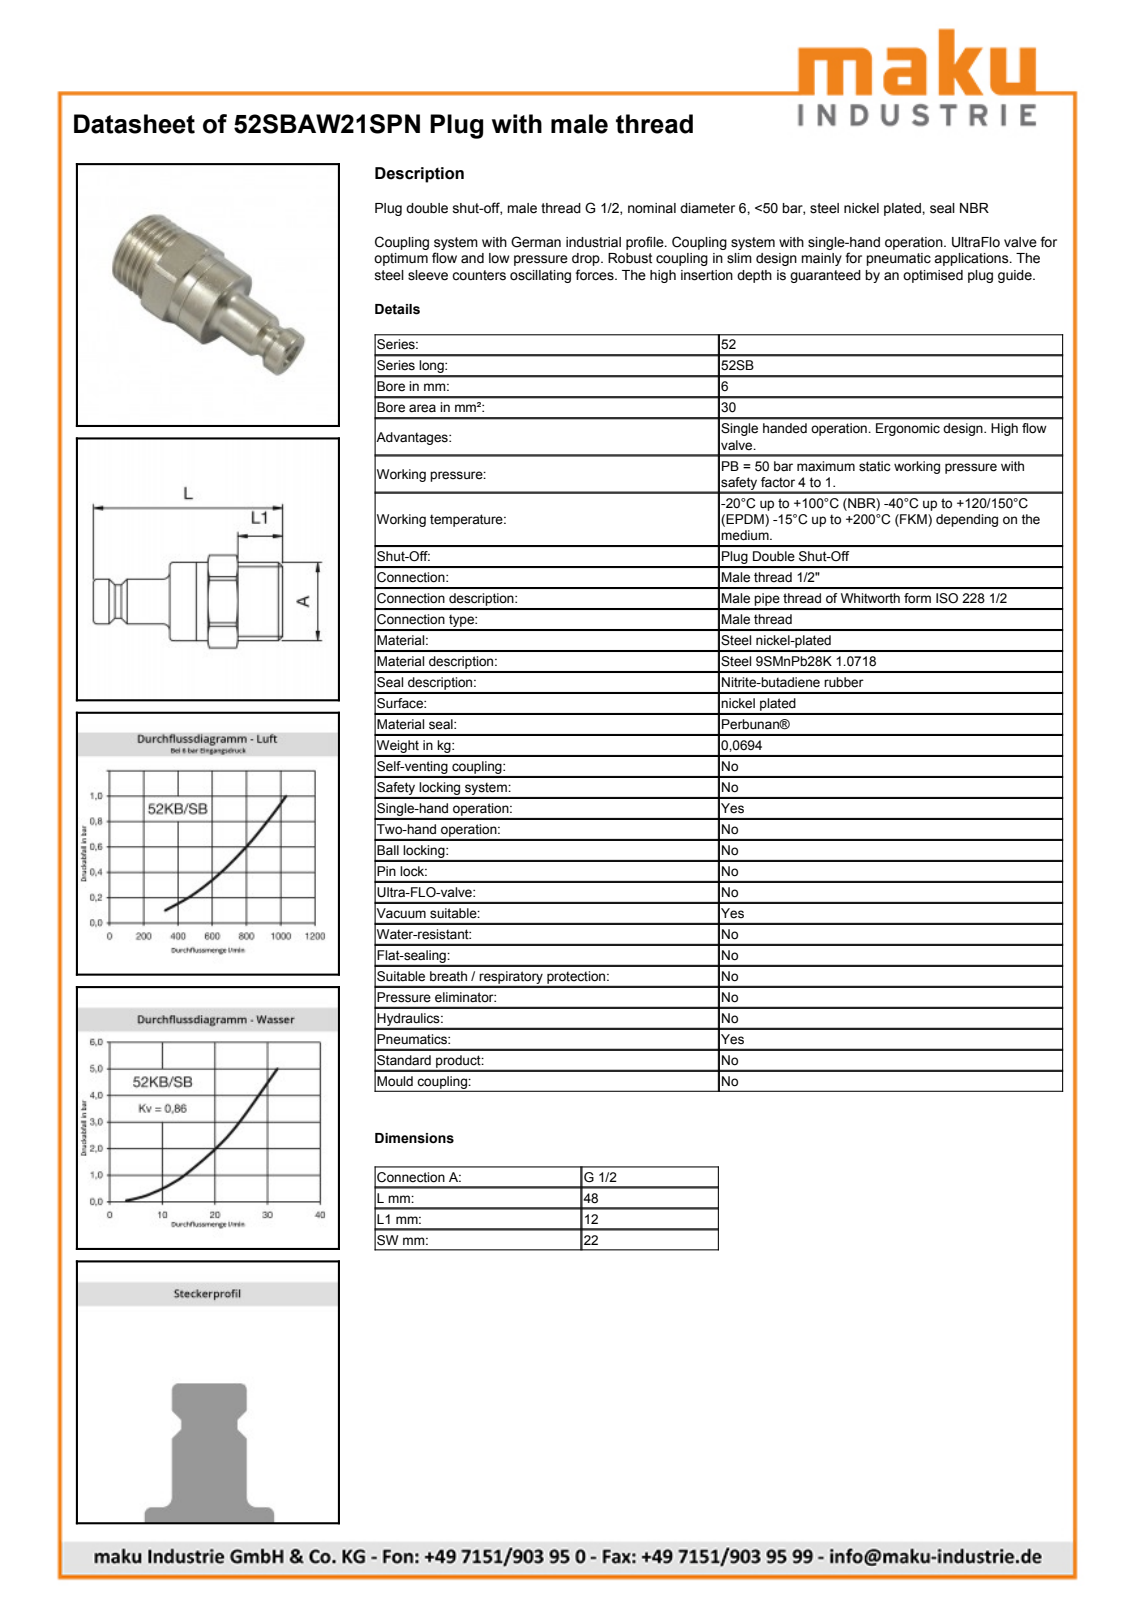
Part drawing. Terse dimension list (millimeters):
name: D105399
written by: Autodesk Inventor 2011 (AUTOMOTIVE_DESIGN)
unit: mm
bodies: 1 solid, 49 faces (14 planar, 15 cylindrical, 20 other)
size: 50.6 × 24.46 × 23.9
volume: 13 063 mm³; area: 4 013 mm²
holes: 1× ⌀17.15
bosses: 1× ⌀21, 1× ⌀20.95, 1× ⌀16.87, 1× ⌀11.95, 1× ⌀8.9
rounds: 1× R12.4
face distances: 22, 30.2, 20.4, 50.6, 38.6, 18.2, 12, 30.6, 10.2, 8
